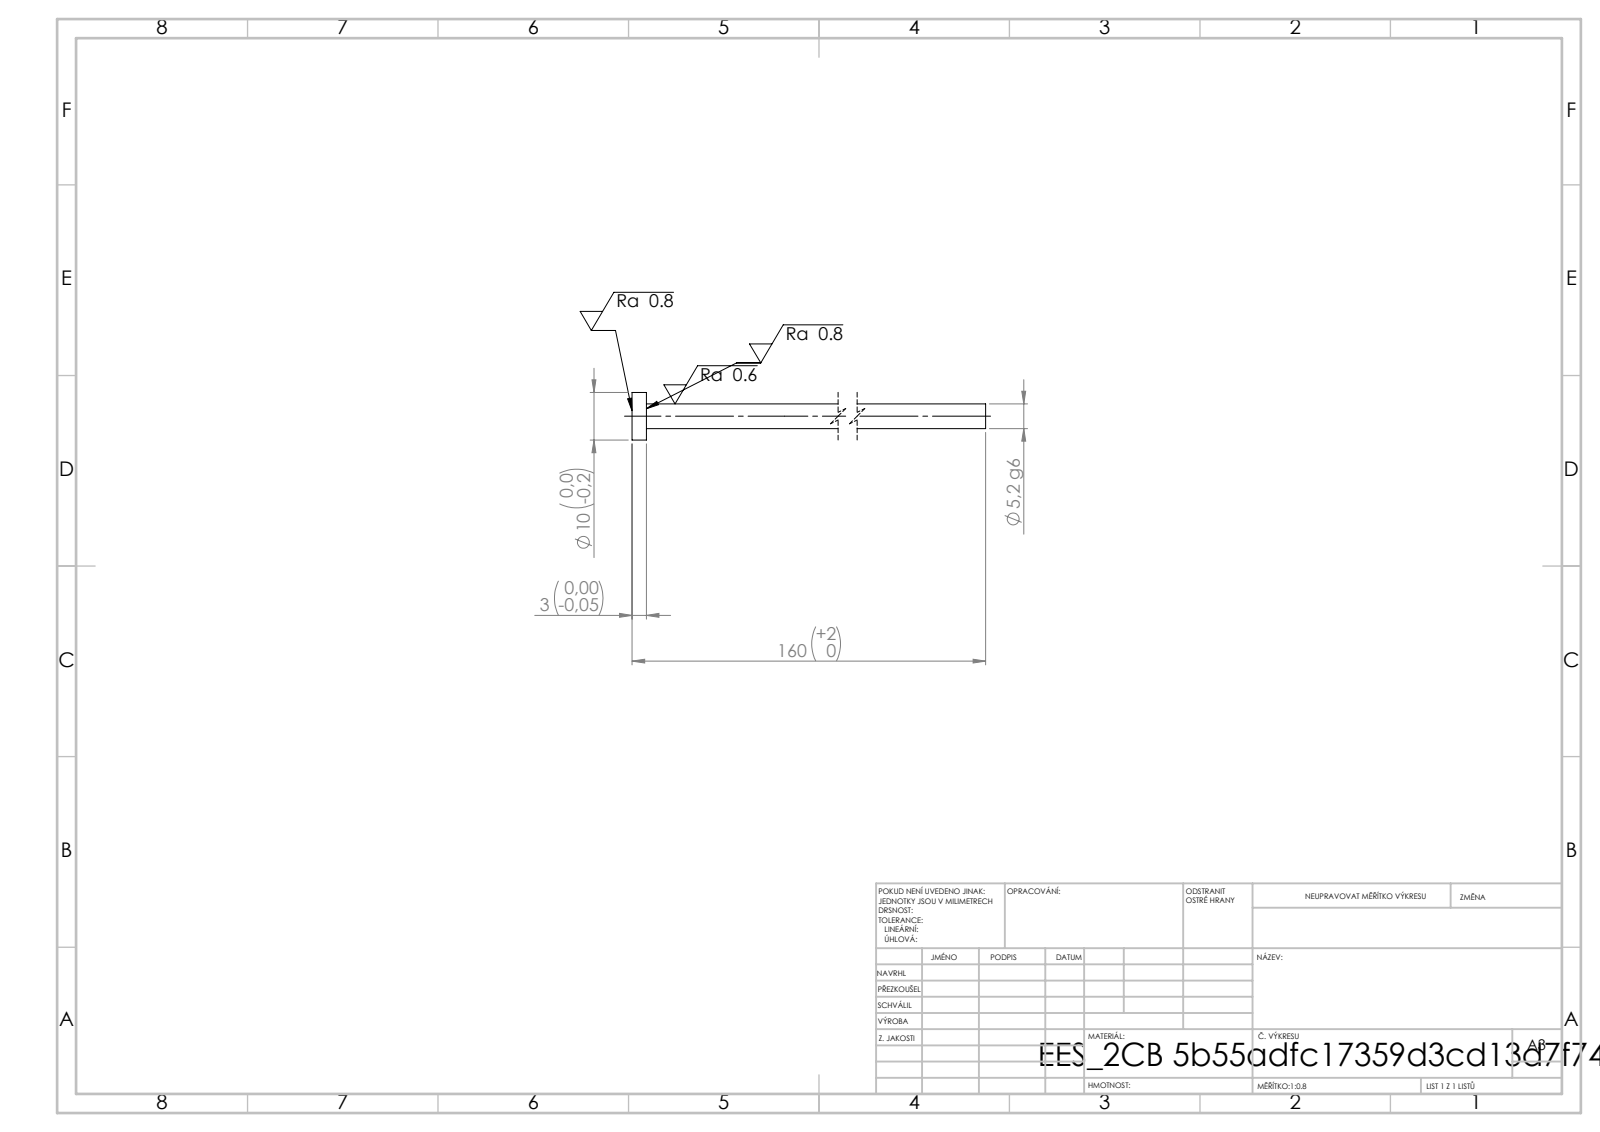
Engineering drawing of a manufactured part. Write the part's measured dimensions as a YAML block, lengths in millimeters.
step_written_by: "SolidWorks 2019 (CONFIG_CONTROL_DESIGN)"
units: millimeters
bodies: {solids: 1, faces: 7, planar: 3, cylindrical: 4, other: 0}
overall_size: [160, 10, 10]
volume: 3570
surface_area: 2816
round_bosses_or_shafts:
  - {diameter: 10, count: 1}
  - {diameter: 5.2, count: 1}
face_to_face_distances: [3, 160, 157]
